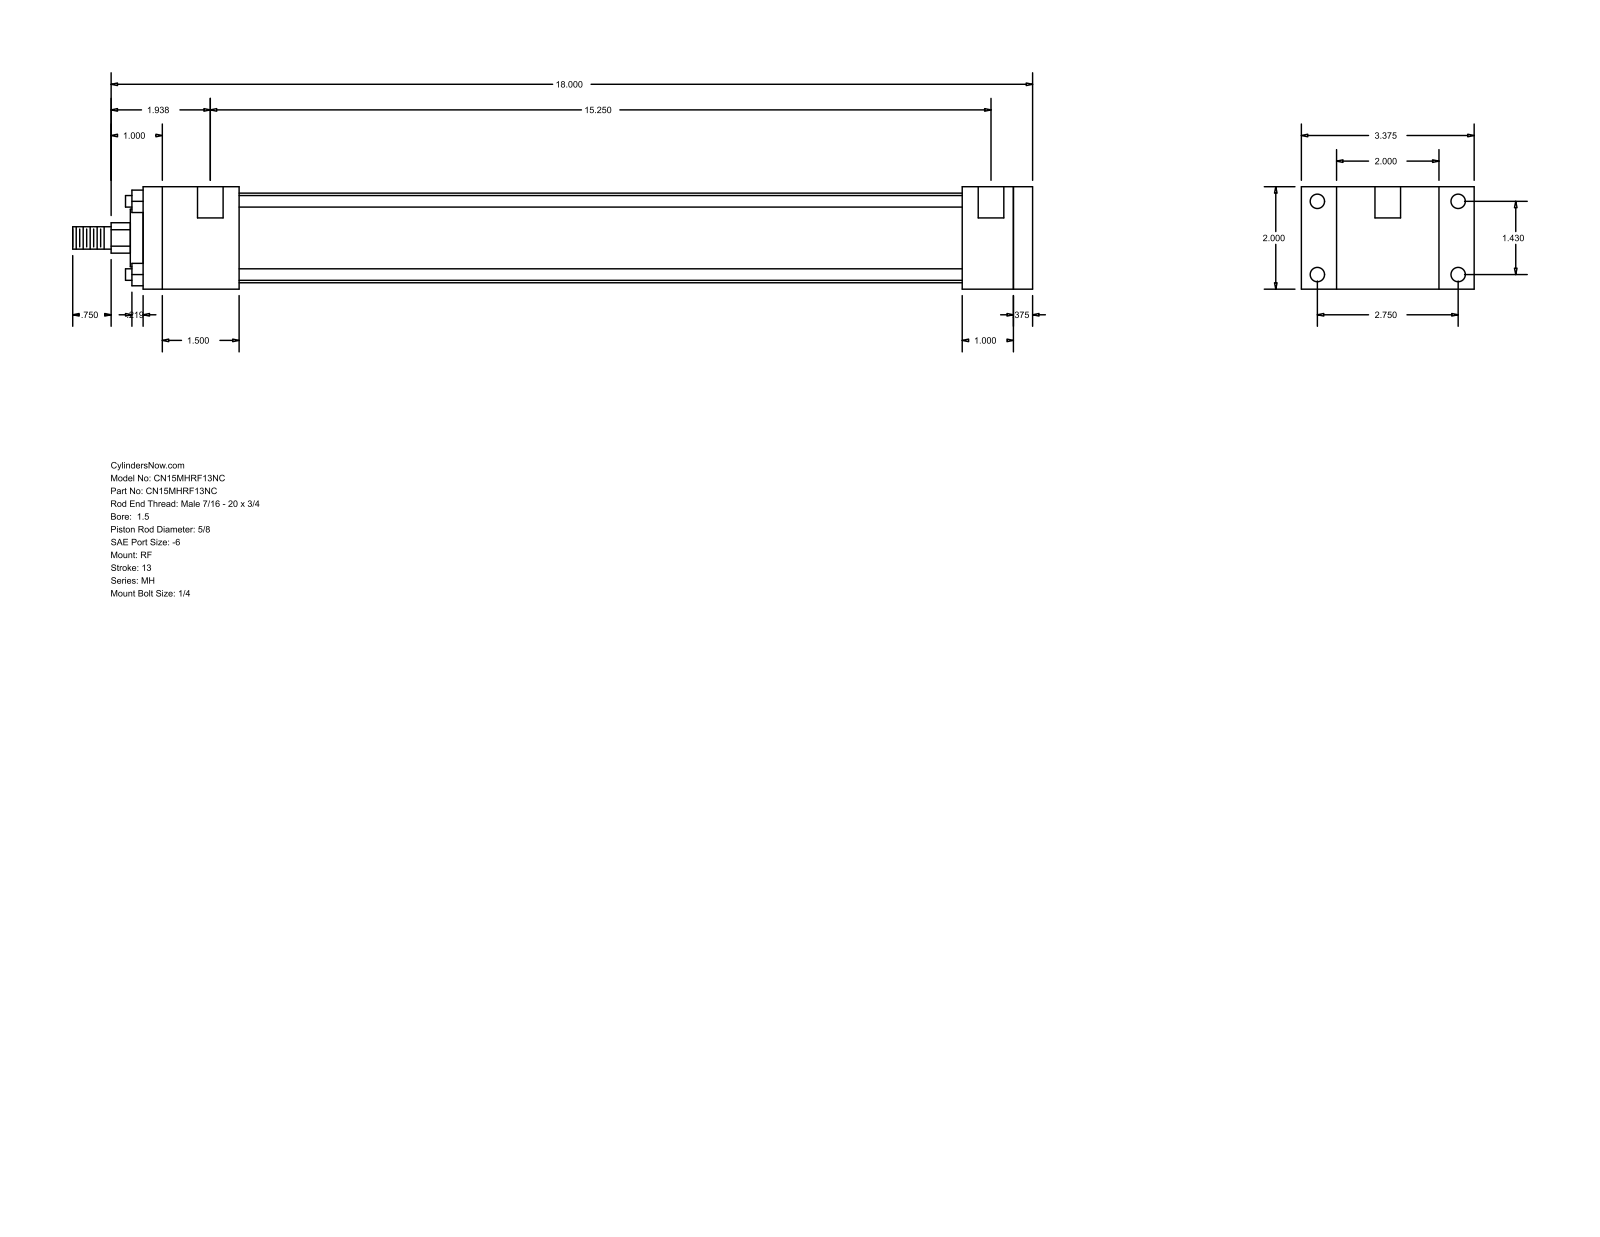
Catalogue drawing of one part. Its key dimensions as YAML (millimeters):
part_name: "MH_RF__0150_0.625"
step_written_by: "GSSL Pune (CONFIG_CONTROL_DESIGN)"
units: millimeters
bodies: {solids: 0, faces: 92, planar: 64, cylindrical: 28, other: 0}
overall_size: [476.25, 85.72, 50.8]
round_holes:
  - {diameter: 5.56, count: 4}
  - {diameter: 7.14, count: 4}
  - {diameter: 12.7, count: 2}
round_bosses_or_shafts:
  - {diameter: 5.71, count: 4}
  - {diameter: 44.45, count: 1}
  - {diameter: 28.57, count: 1}
  - {diameter: 15.88, count: 1}
  - {diameter: 11.11, count: 1}
partial_cylinders:
  - {radius: 7.54, count: 1}
face_to_face_distances: [50.8, 9.52, 441.32, 431.8, 34.93, 17.46, 68.26, 406.39, 25.41, 47.62]
hole_center_spacings: [36.32, 69.84, 78.72, 390.52, 3.17, 387.35]
